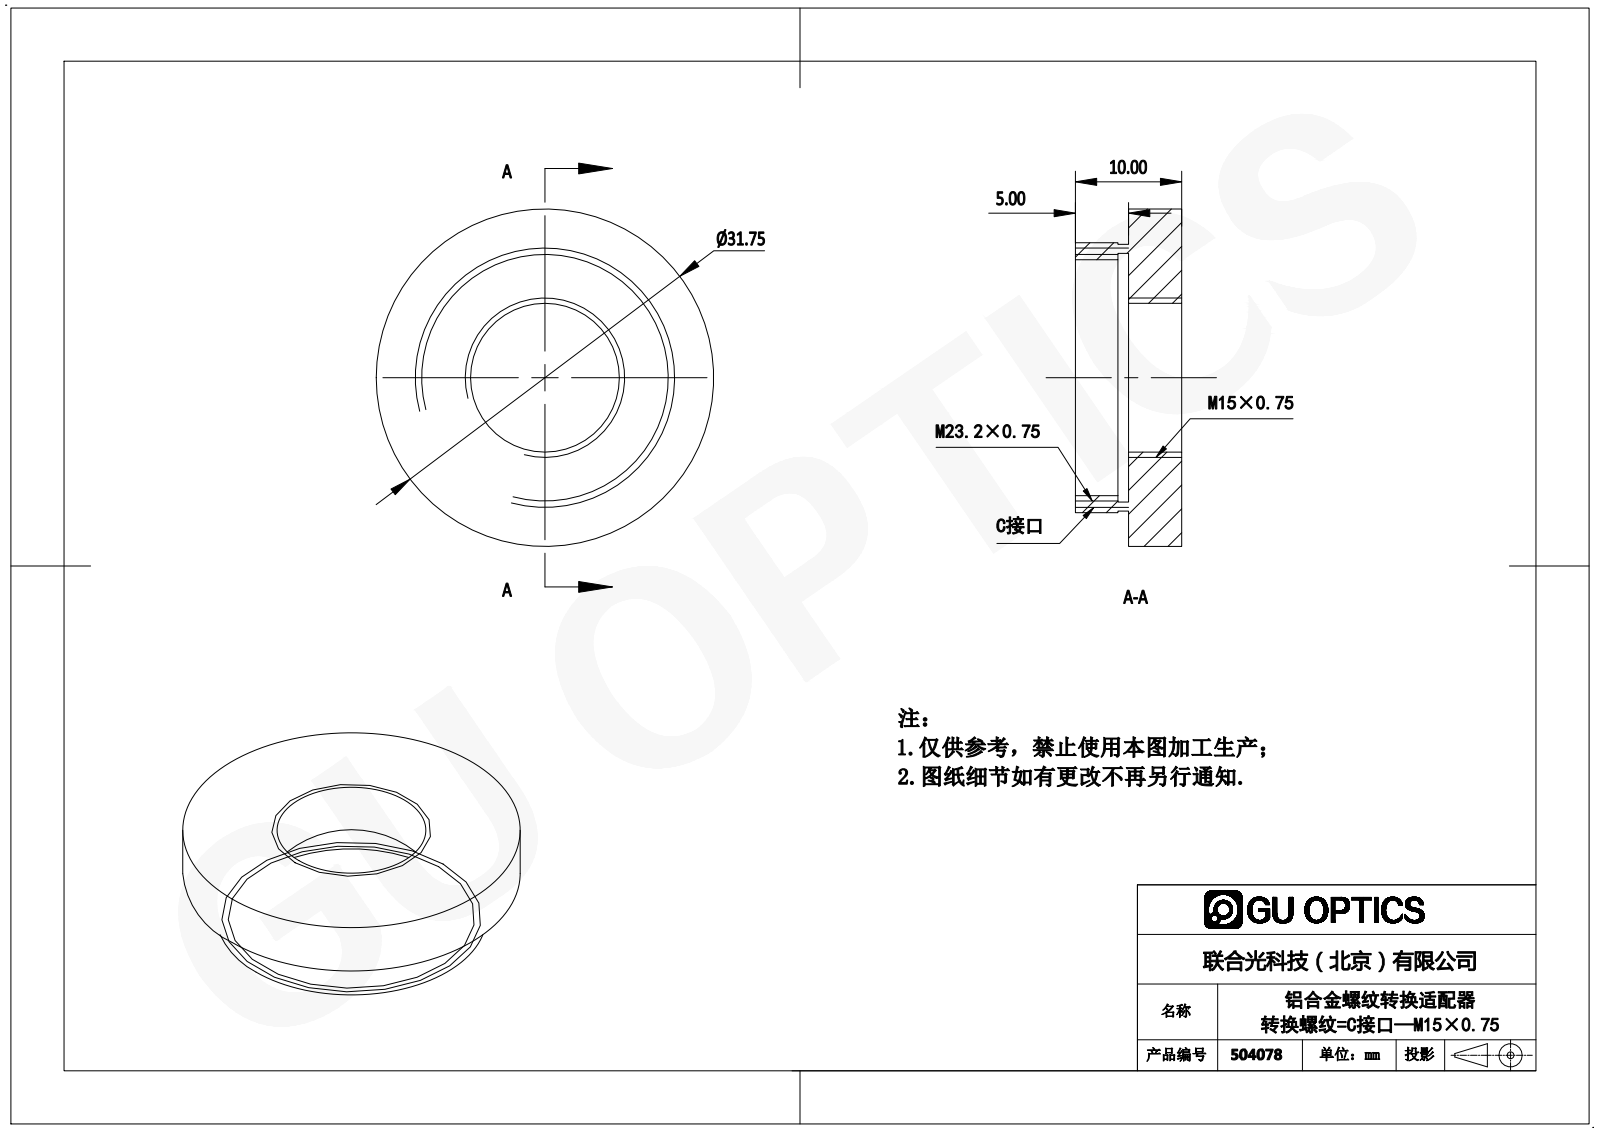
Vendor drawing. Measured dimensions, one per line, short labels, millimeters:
name: 504078
written by: SolidWorks 2016 (AUTOMOTIVE_DESIGN)
unit: mm
bodies: 1 solid, 18 faces (6 planar, 12 cylindrical, 0 other)
size: 31.75 × 31.75 × 10
volume: 3 732 mm³; area: 2 854 mm²
holes: 1× ⌀14, 1× ⌀22.2, 1× ⌀23.4
bosses: 1× ⌀31.75, 1× ⌀25.4, 1× ⌀25.1
face distances: 5, 10, 4, 1, 6
